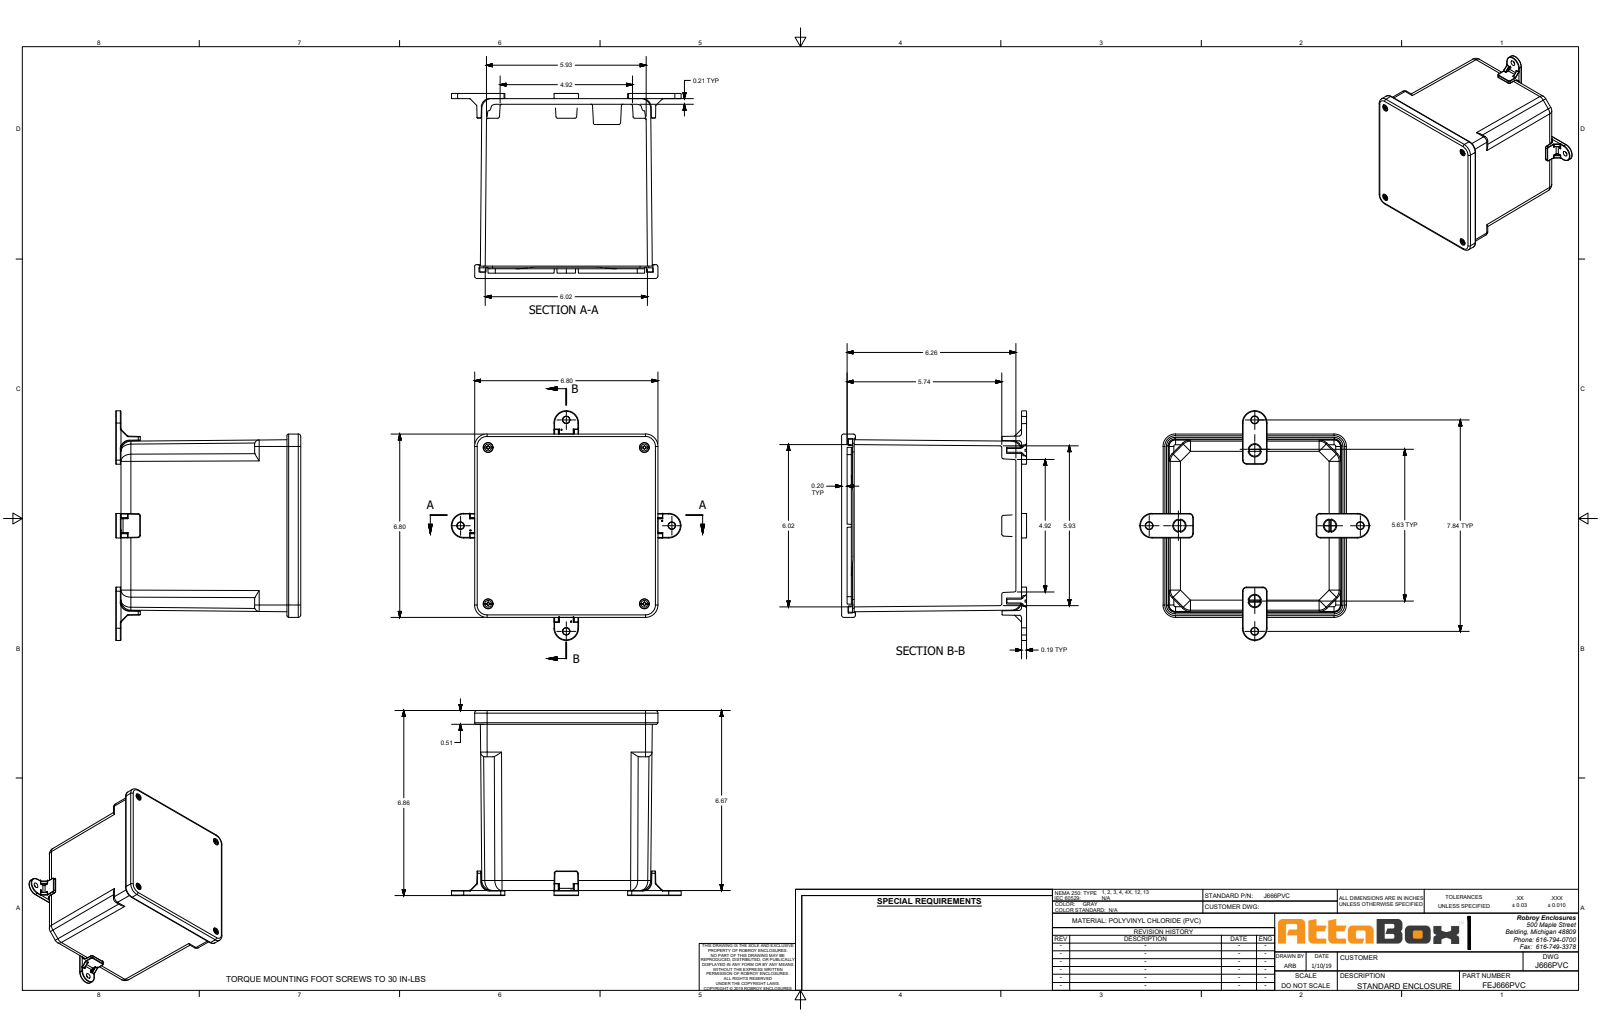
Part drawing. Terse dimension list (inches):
name: J666PVC
written by: SolidWorks 2018 (AUTOMOTIVE_DESIGN)
unit: in
bodies: 23 solids, 1189 faces (479 planar, 361 cylindrical, 349 other)
size: 8.52 × 8.52 × 6.864
volume: 50.53 in³; area: 539.7 in²
holes: 8× ⌀0.2, 4× ⌀0.13, 4× ⌀0.14, 4× ⌀0.175, 4× ⌀0.223, 4× ⌀0.25, 4× ⌀0.276, 4× ⌀0.335, 4× ⌀0.37, 1× ⌀0.406
bosses: 4× ⌀0.354, 4× ⌀0.325, 4× ⌀0.224, 4× ⌀0.187, 4× ⌀0.177
rounds: 84× R0.02, 20× R0.25, 16× R0.005, 16× R0.375, 15× R0.063, 12× R0.08, 12× R0.094, 9× R0.062
face distances: 0.18, 6.674, 6.474, 0.2, 0.21, 6.264, 6.464, 6.432, 6.222, 0.042
hole spacings: 2.902, 6.391, 5.8, 5.813, 3.953, 0.013, 2.902, 2.915
